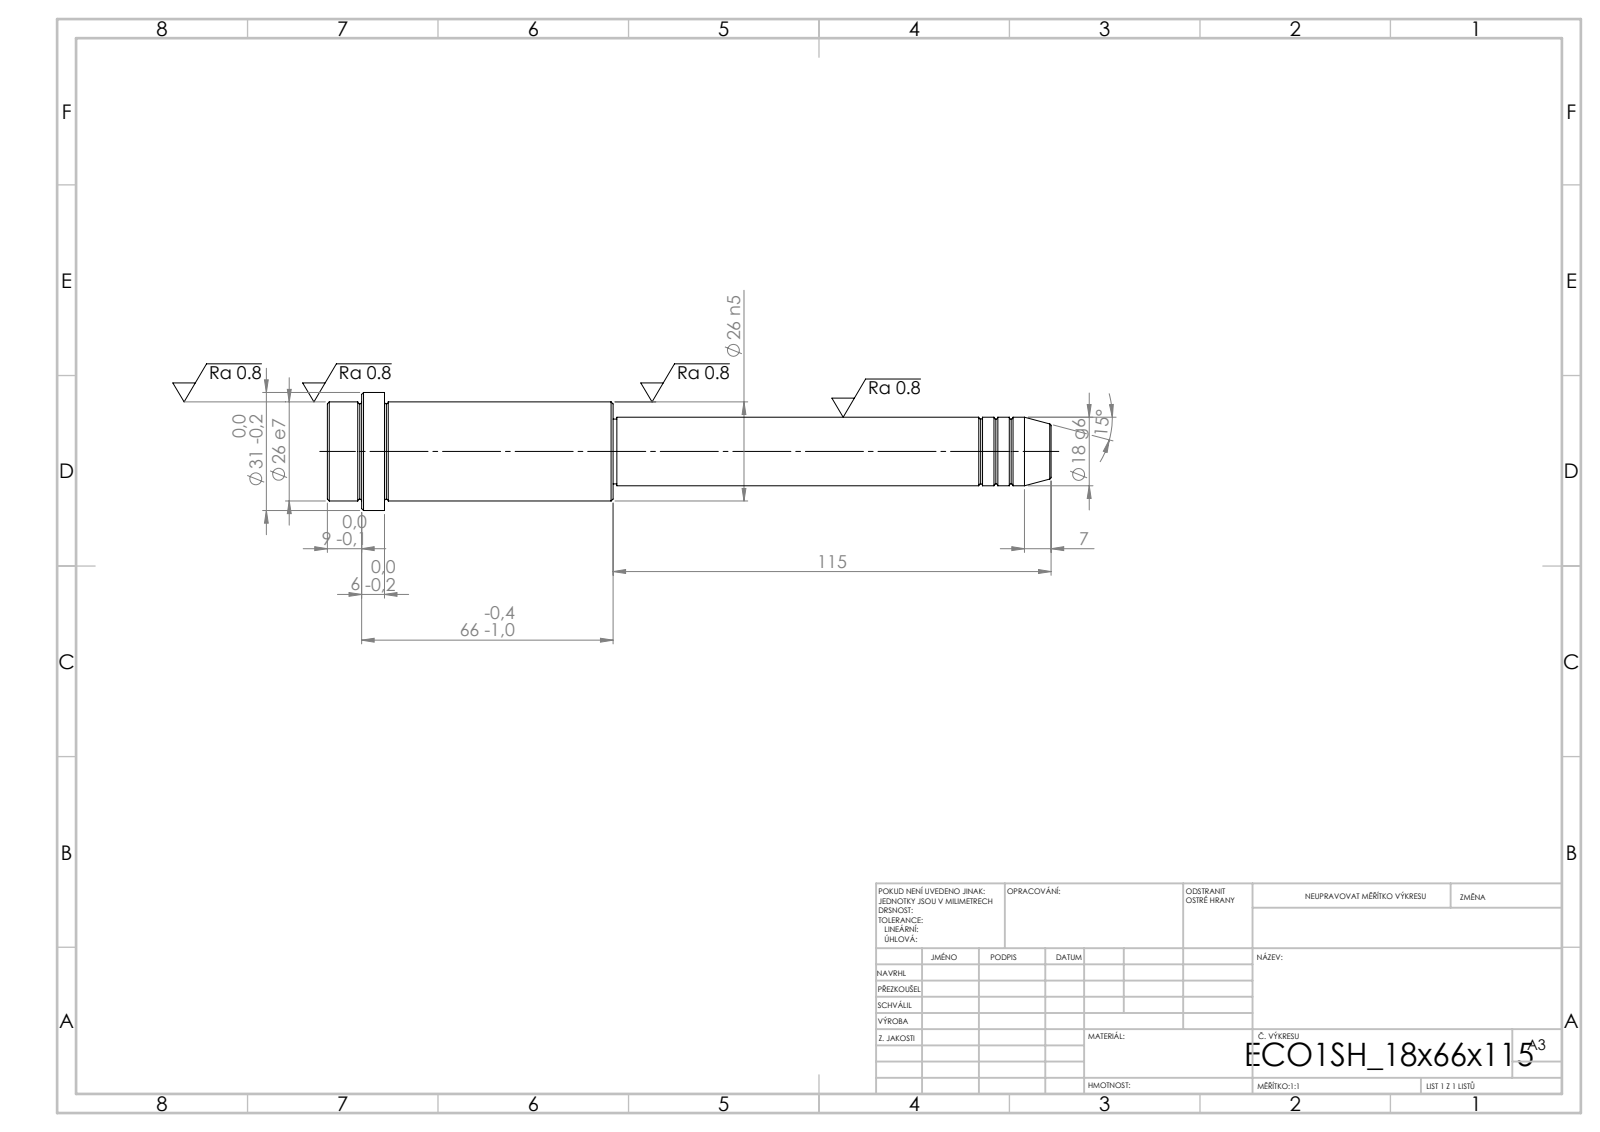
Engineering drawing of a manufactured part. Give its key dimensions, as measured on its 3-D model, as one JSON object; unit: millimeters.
{"step_written_by": "SolidWorks 2019 (CONFIG_CONTROL_DESIGN)", "units": "millimeters", "bodies": {"solids": 1, "faces": 52, "planar": 6, "cylindrical": 16, "other": 30}, "overall_size": [190, 31, 31], "volume_mm3": 69892, "surface_area_mm2": 14253, "round_bosses_or_shafts": [[31, 1], [26, 1], [18, 1], [17, 1]], "face_to_face_distances": [75, 60, 15, 66, 6, 9, 115, 175, 181, 190]}
